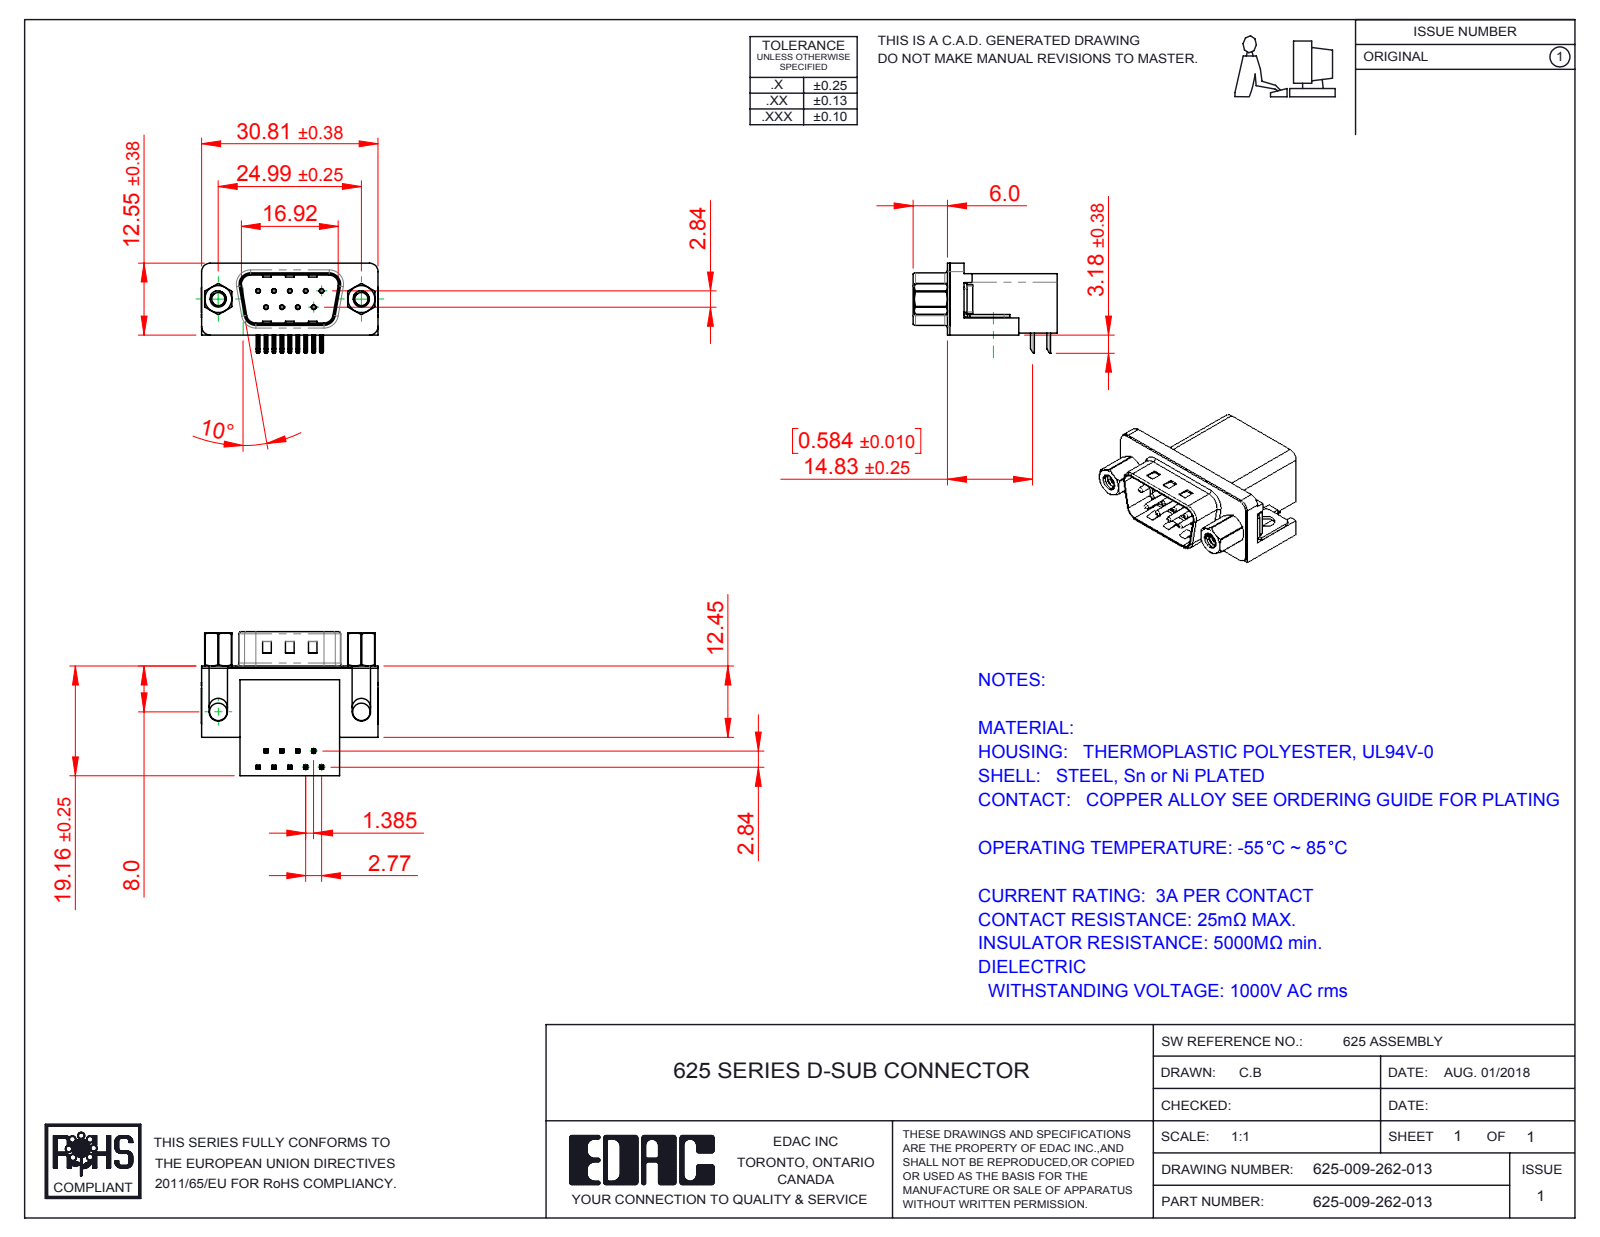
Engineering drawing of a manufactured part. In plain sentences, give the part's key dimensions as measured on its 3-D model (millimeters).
The part is named "625 Shell_9 Socket; 625 Housing_9 Socket; 625-009-262-013; 625 4-40 Hex Standoff 5 (+4 more)". Its 3-D file was written by "SolidWorks 2016 (CONFIG_CONTROL_DESIGN)". It is 17 solids with 1119 faces: 595 planar, 389 cylindrical and 135 other. Overall it measures 30.89 by 25.16 by 15.73 millimeters. Its volume is 4 686 cubic millimeters and its surface area 5 421 square millimeters. Round holes: 9 of diameter 0.35, 9 of diameter 0.8, 2 of diameter 2.26, 2 of diameter 2.29, 2 of diameter 3.05, 2 of diameter 4, 2 of diameter 4.8, 2 of diameter 5. Round bosses or shafts: 9 of diameter 0.75, 2 of diameter 4.9, 2 of diameter 4.75, 2 of diameter 3.9, 2 of diameter 2.79. Partial cylindrical surfaces (rounded edges, fillets, slot ends): 44 of radius 0.25, 18 of radius 0.12, 16 of radius 1, 9 of radius 0.5, 8 of radius 1.5, 8 of radius 1.6, 4 of radius 0.9, 4 of radius 2. The main face-to-face distances are 0.4, 10.34, 18.76, 19.16, 16.26, 2.5, 2.9, 0.5, 0.35, 10.69. The hole center spacings are 3.16, 2.77, 5.54, 5.03, 5.04, 8.31, 7.48, 7.49.
